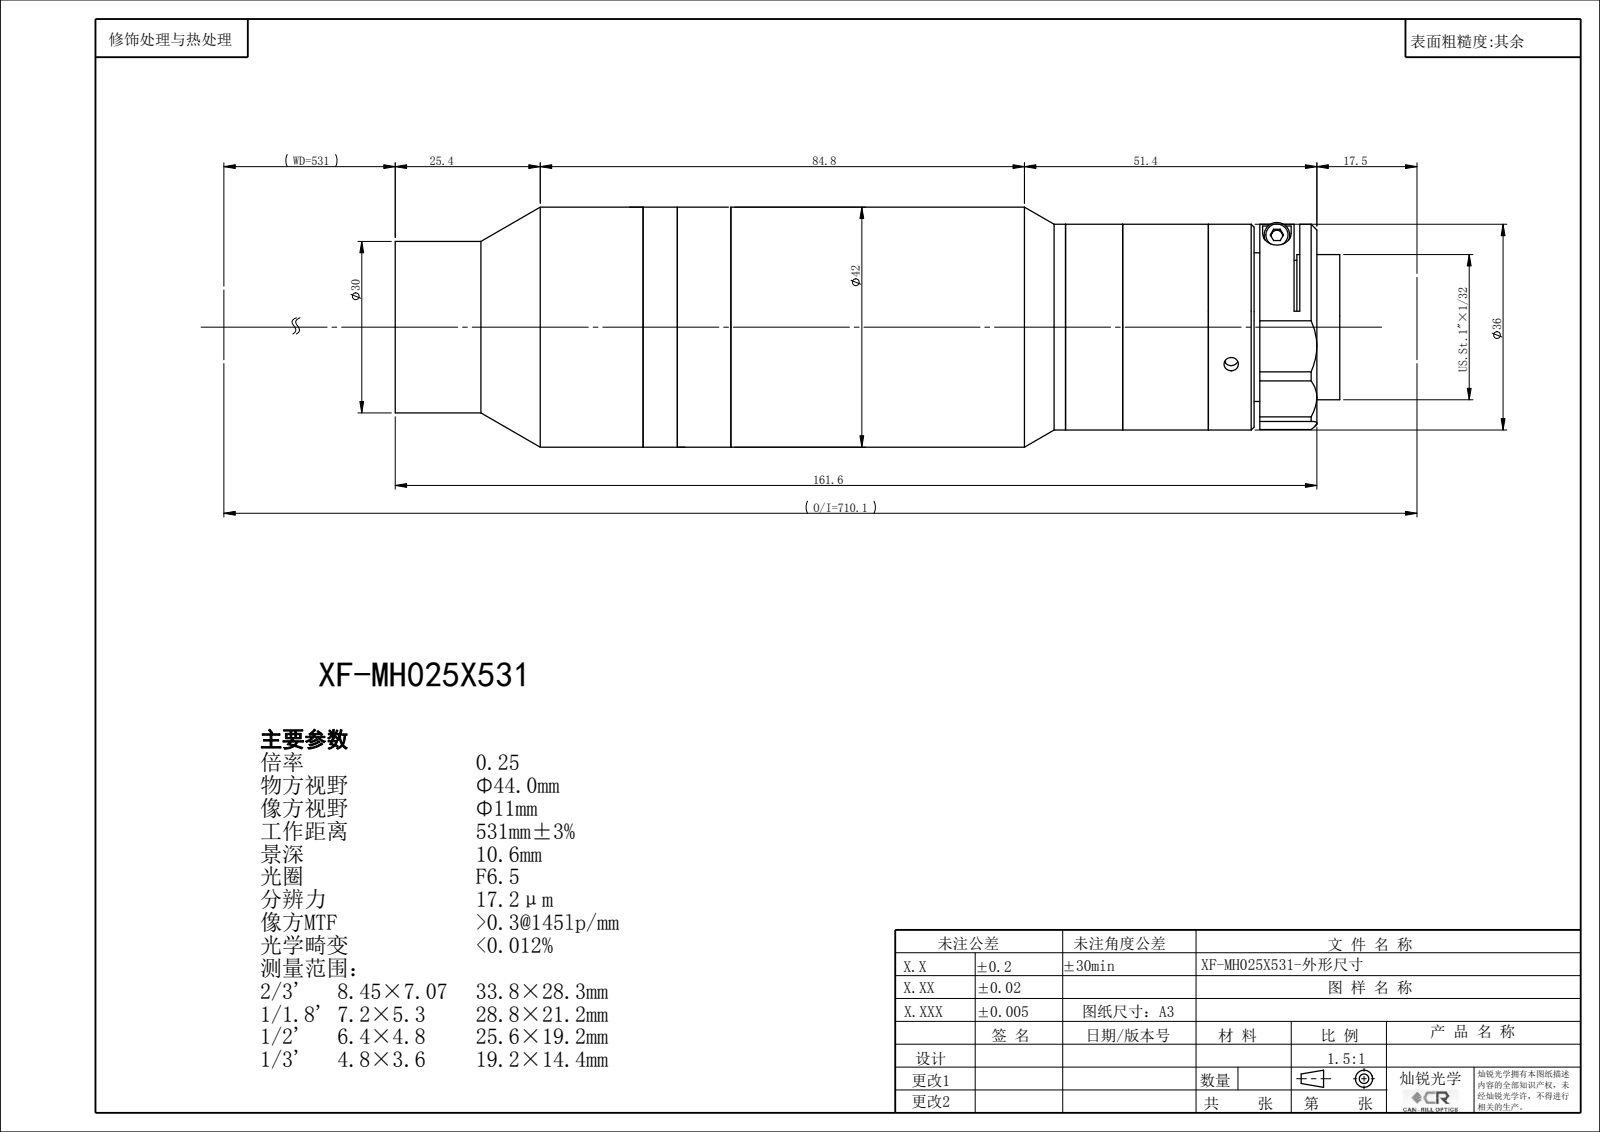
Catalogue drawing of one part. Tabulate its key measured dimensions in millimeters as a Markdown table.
| quantity | value |
| --- | --- |
| part name | XF-MH025X531 |
| STEP written by | SolidWorks 2022 (CONFIG_CONTROL_DESIGN) |
| units | millimeters |
| bodies | 0 solids, 130 faces (62 planar, 44 cylindrical, 24 other) |
| overall size | 165.56 × 42 × 42 |
| round holes (diameter × count) | 2.5 × 3, 22.4 × 1, 24 × 1, 26.4 × 1 |
| round bosses / shafts (diameter × count) | 42 × 1, 36 × 1, 34 × 1, 30 × 1, 25.4 × 1 |
| main face-to-face distances | 19.21, 1.5, 17.71, 15, 32.71, 34.21, 10, 25, 42.71, 44.21 |
